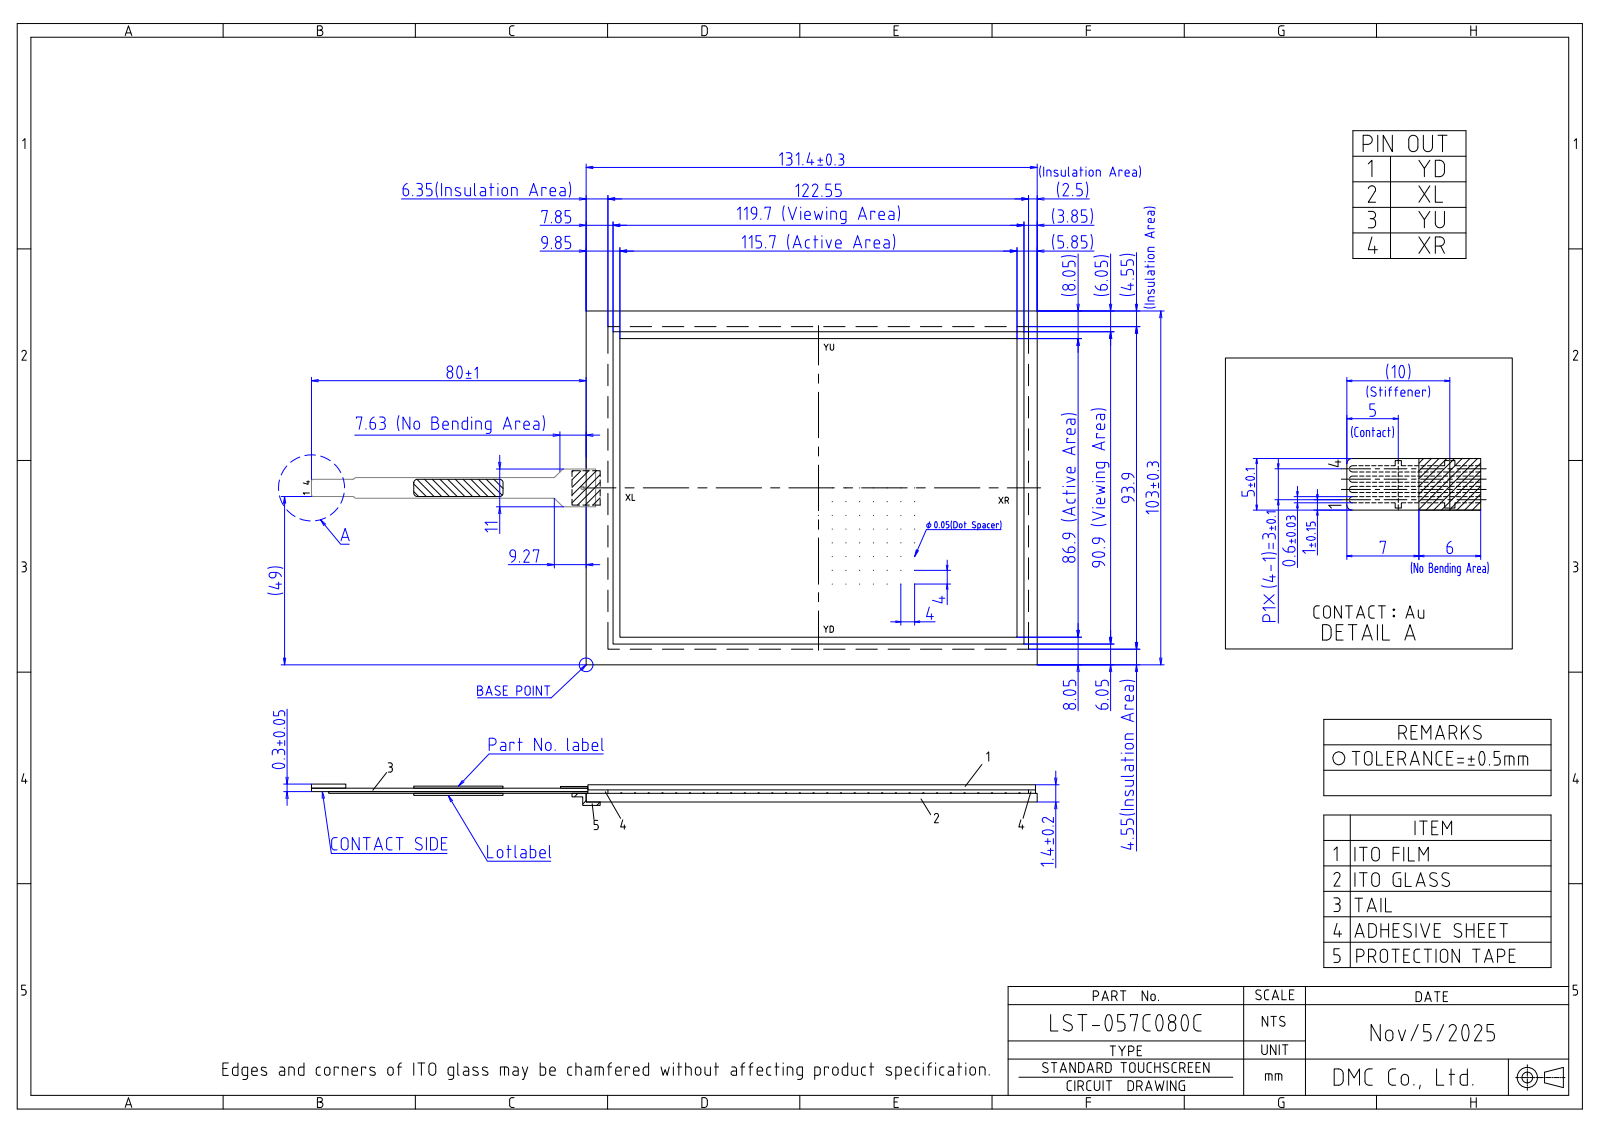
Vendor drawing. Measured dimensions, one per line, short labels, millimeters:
name: LST-057C080C-2
written by: Autodesk Inventor 2020 (CONFIG_CONTROL_DESIGN)
unit: mm
bodies: 2 solids, 52 faces (46 planar, 6 cylindrical, 0 other)
size: 211.4 × 103 × 1.9
volume: 18 928 mm³; area: 28 849 mm²
rounds: 4× R0.3, 2× R0.5
face distances: 1.4, 1.3, 1.5, 1.6, 103, 131.4, 0.5, 0.6, 0.4, 1.9
